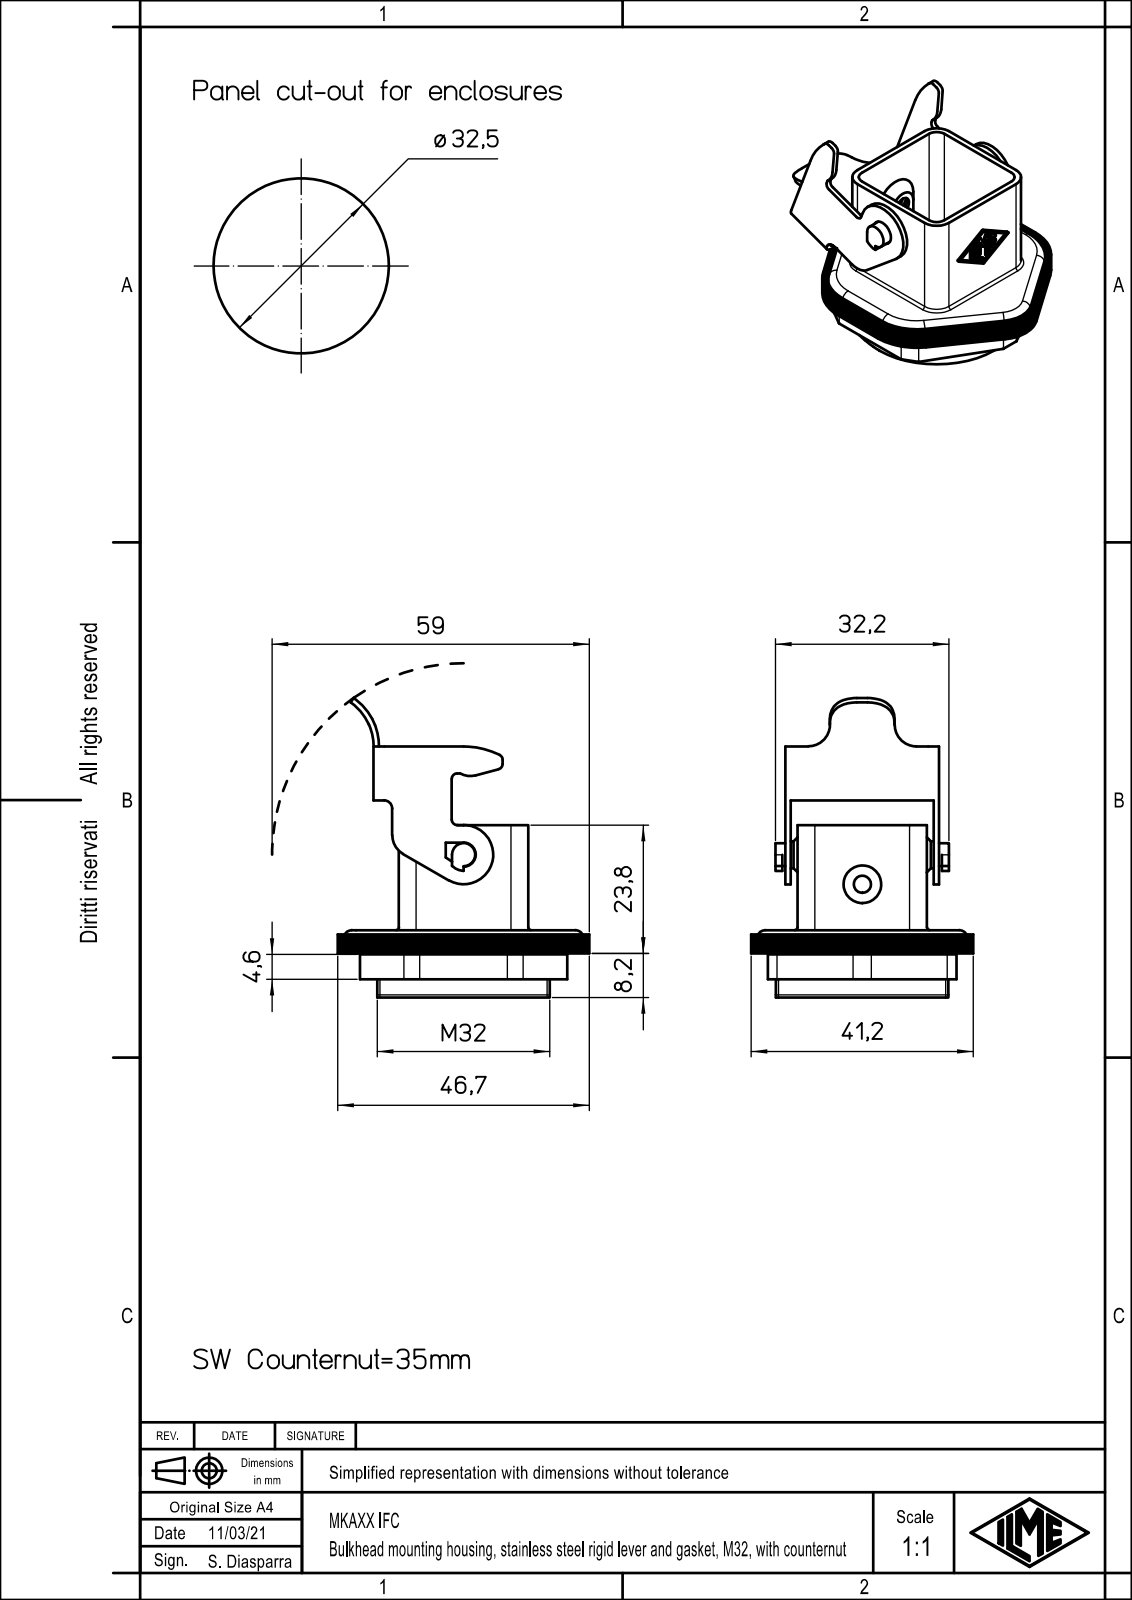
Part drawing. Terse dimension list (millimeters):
name: MKAXX_IFC; Counternut
written by: Creo Elements/Direct Modeling 20.1B 02-Apr-2019 (C) Parametric Technology GmbH (AUTOMOTIVE_DESIGN)
unit: mm
bodies: 2 solids, 233 faces (122 planar, 94 cylindrical, 17 other)
size: 57.66 × 41.2 × 39.4
volume: 11 879 mm³; area: 12 370 mm²
holes: 1× ⌀3.2, 1× ⌀7
bosses: 1× ⌀32, 1× ⌀5, 1× ⌀4.3
rounds: 15× R0.25, 7× R1.5, 6× R1, 6× R2, 4× R3.2, 4× R4, 4× R9.1, 4× R10.1
face distances: 1.39, 22.61, 21.22, 24, 3.64, 24.86, 1, 27.5, 2.64, 23.86
